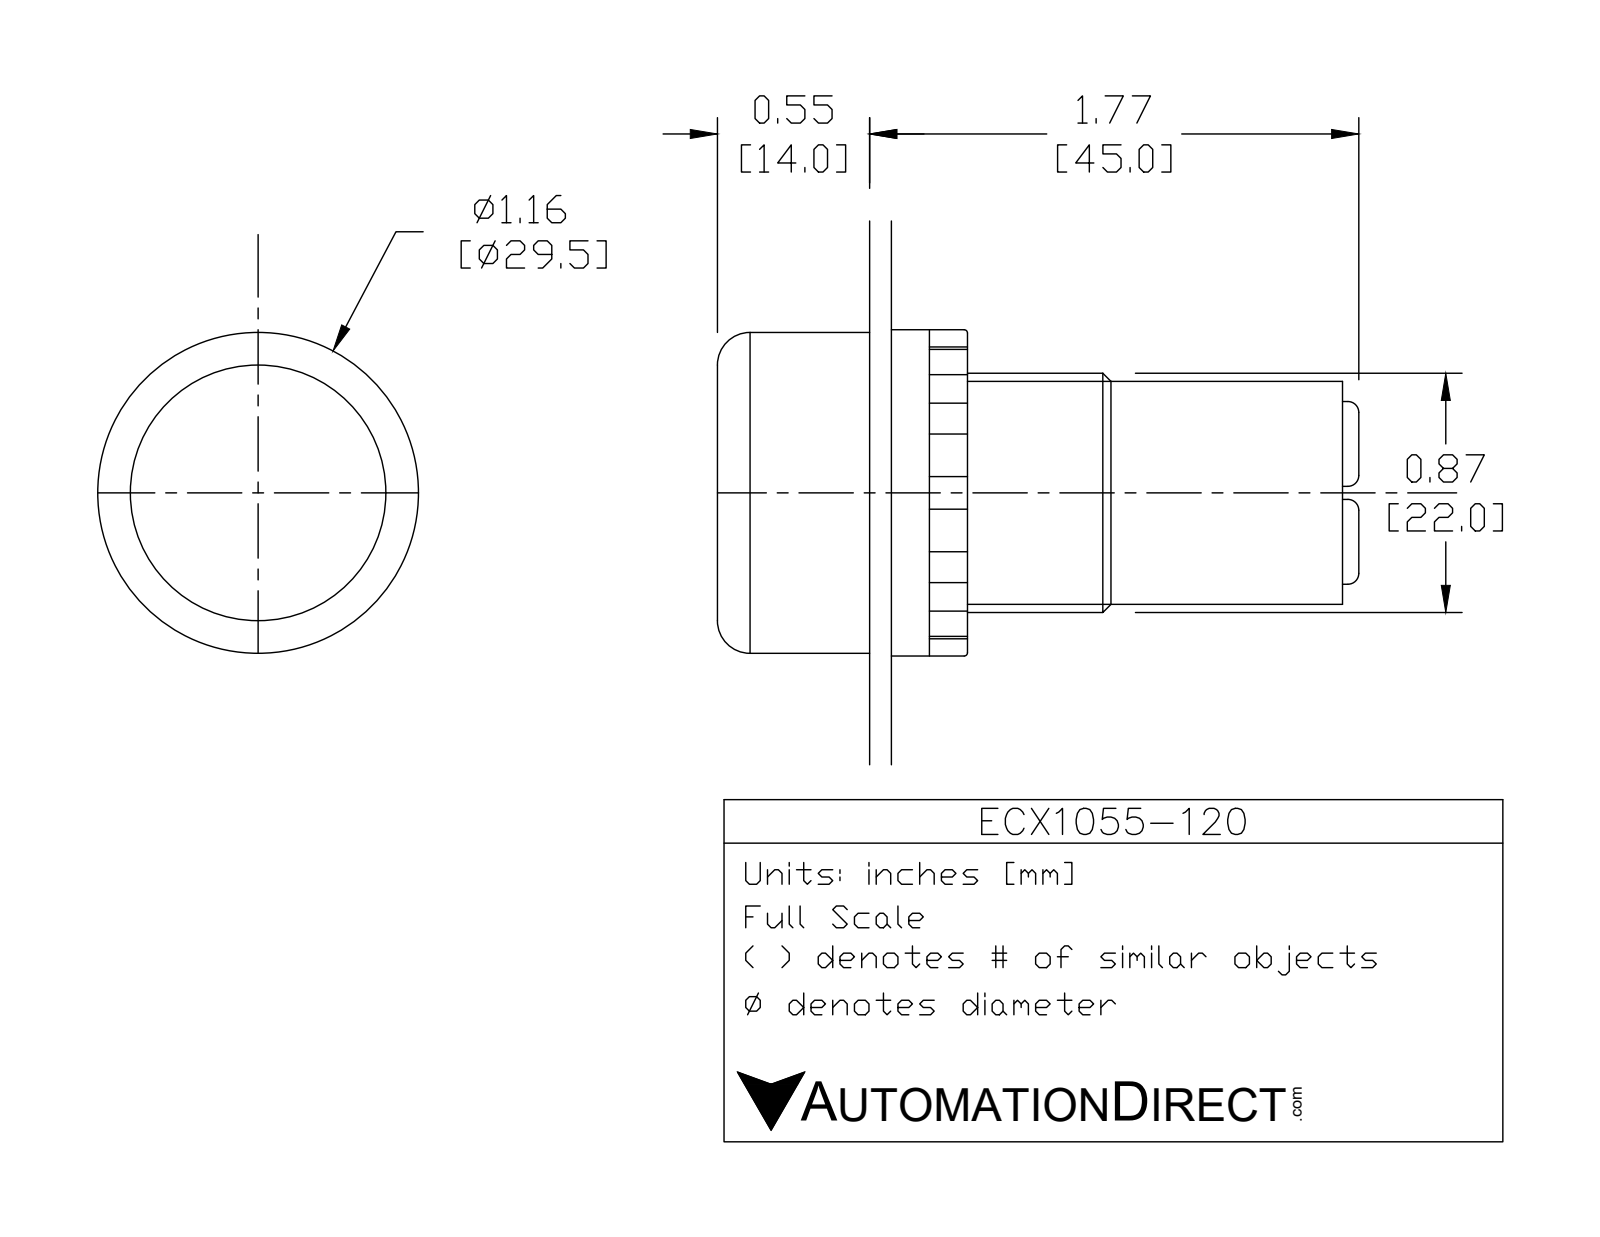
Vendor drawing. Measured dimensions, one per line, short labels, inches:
name: ECX1055-120
written by: SolidWorks 2017 (AUTOMOTIVE_DESIGN)
unit: in
bodies: 6 solids, 125 faces (63 planar, 41 cylindrical, 21 other)
size: 2.323 × 1.181 × 1.181
volume: 1.605 in³; area: 15.04 in²
holes: 2× ⌀0.217, 1× ⌀0.886
bosses: 2× ⌀0.157, 1× ⌀1.181, 1× ⌀1.142, 1× ⌀1.043, 1× ⌀0.866, 1× ⌀0.787
rounds: 12× R0.039, 1× R0.354
face distances: 0.531, 0.02, 0.551, 0.787, 0.236, 0.256, 1.535, 0.276, 0.512, 1.063
hole spacings: 0.182, 0.364
